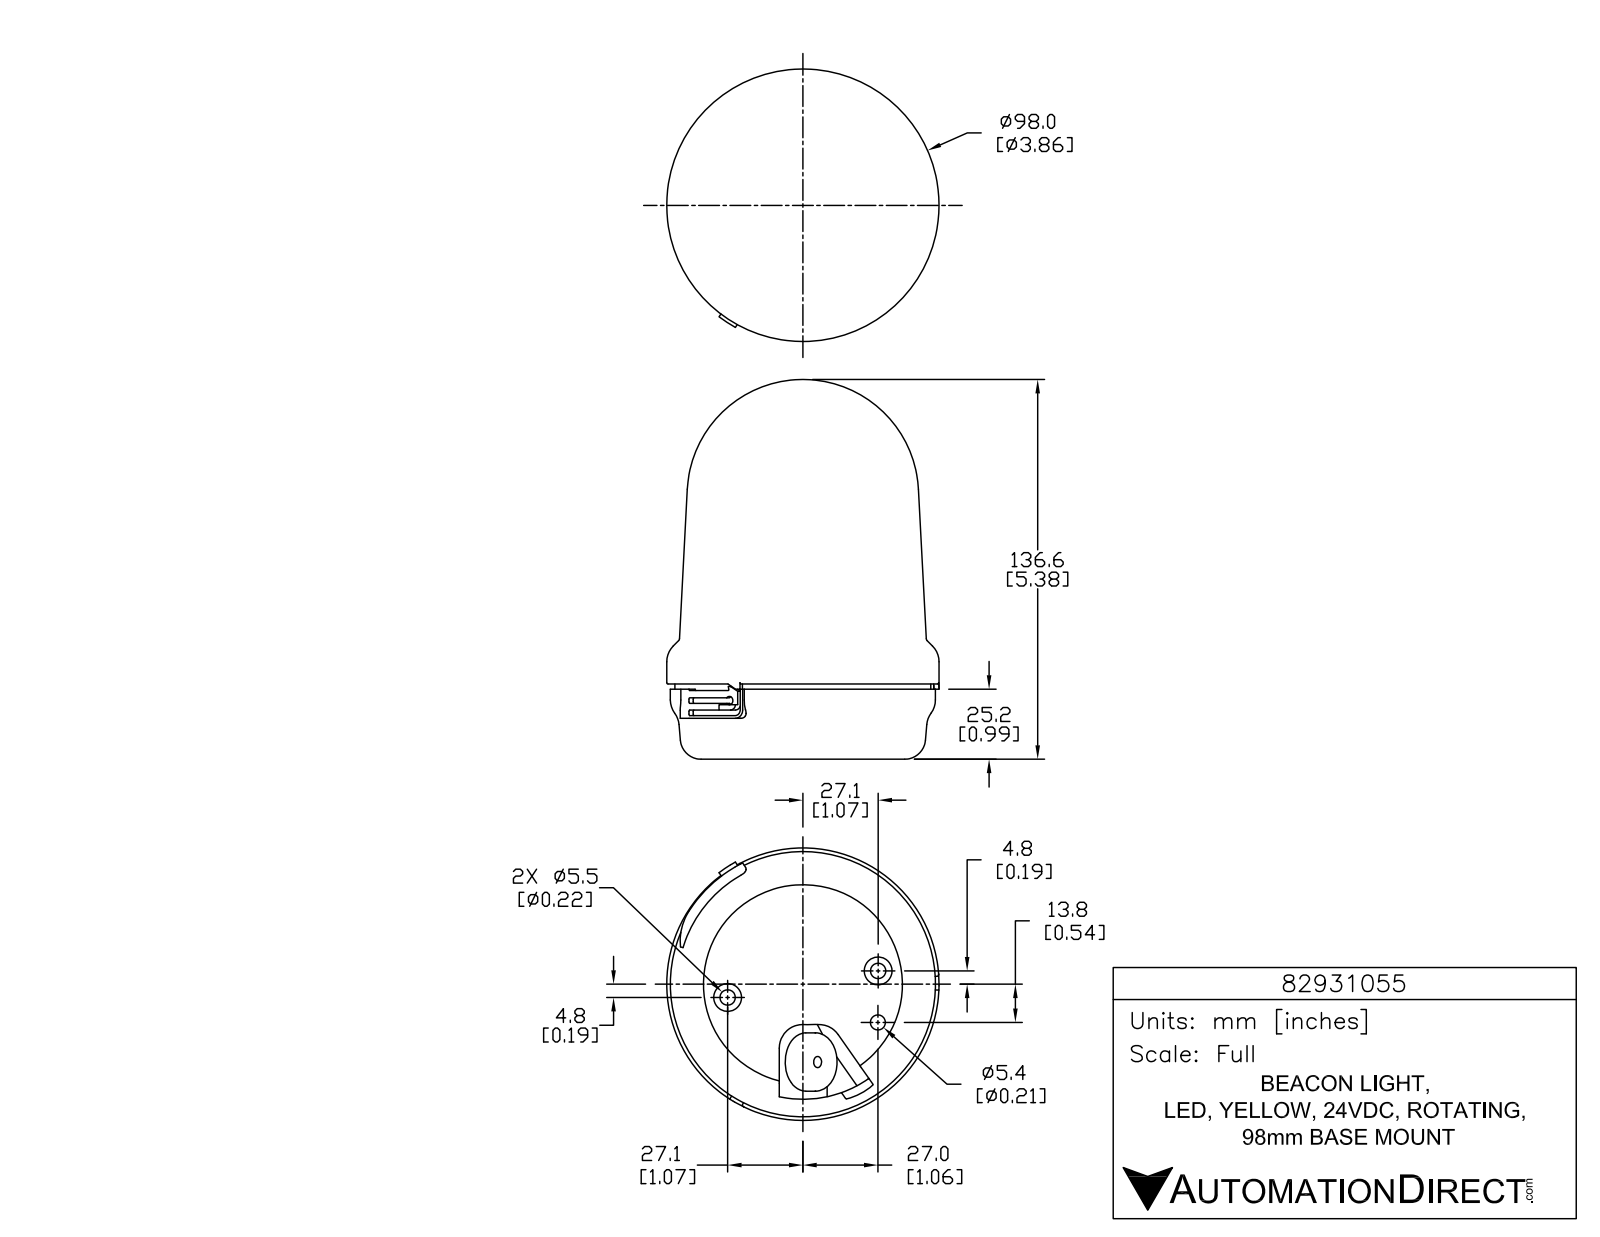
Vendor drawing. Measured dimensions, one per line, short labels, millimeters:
name: 82931055
written by: SolidWorks 2015 (AUTOMOTIVE_DESIGN)
unit: mm
bodies: 1 solid, 872 faces (566 planar, 204 cylindrical, 102 other)
size: 136.6 × 98 × 98
volume: 732 300 mm³; area: 47 520 mm²
holes: 3× ⌀1.5, 2× ⌀5.5, 1× ⌀4, 1× ⌀5.4, 1× ⌀71.6
bosses: 3× ⌀8.6, 3× ⌀2.1, 2× ⌀10, 1× ⌀98, 1× ⌀95.4, 1× ⌀92.1, 1× ⌀21
rounds: 9× R0.1, 6× R0.1, 6× R0.3, 6× R0.3, 6× R0.3, 6× R5, 5× R0.5, 4× R1
face distances: 26.5, 24.7, 1.9, 0.5, 25.2, 27.1, 6, 14.7, 14.2, 10.5
hole spacings: 27.5, 18.5, 30.3, 54.8, 55
